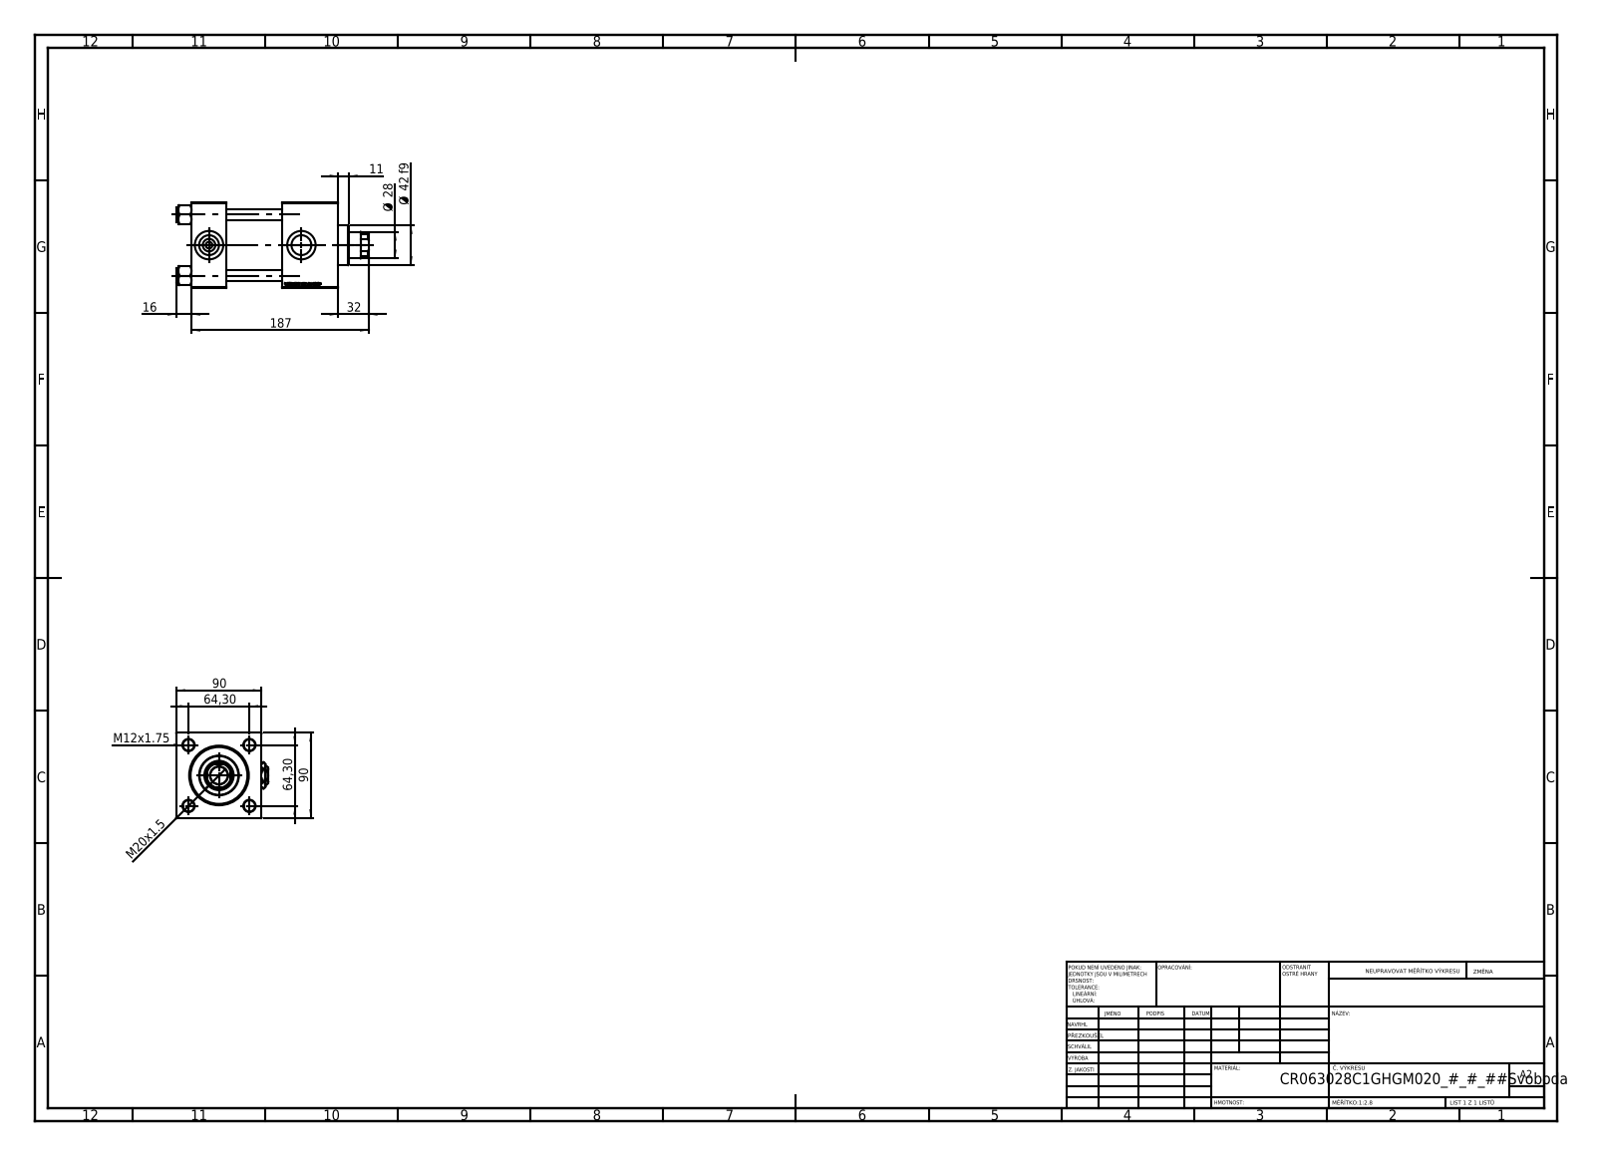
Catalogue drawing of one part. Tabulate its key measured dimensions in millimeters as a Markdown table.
| quantity | value |
| --- | --- |
| part name | NUT_M5_C; Zatka_pro_OIL_PORT; V215CR_C_Body; V215CR_C_TYCINKA (+2 more) |
| STEP written by | SolidWorks 2019 (CONFIG_CONTROL_DESIGN) |
| units | millimeters |
| bodies | 12 solids, 1196 faces (550 planar, 90 cylindrical, 556 other) |
| overall size | 203 × 97 × 90 |
| volume | 942 456 mm³ |
| surface area | 181 253 mm² |
| round holes (diameter × count) | 12 × 4, 7 × 2, 20.96 × 2, 30 × 2, 18.5 × 1, 28 × 1, 31 × 1, 50 × 1, 60 × 1, 63 × 1 |
| round bosses / shafts (diameter × count) | 15 × 4, 69 × 1, 42 × 1 |
| partial cylindrical surfaces (radius × count) | 13.5 × 1 |
| main face-to-face distances | 90, 59, 37, 118, 155, 96, 126.3, 89.3, 30.3, 28.7 |
| hole center spacings | 45.47, 64.3, 90.93, 97.5 |
